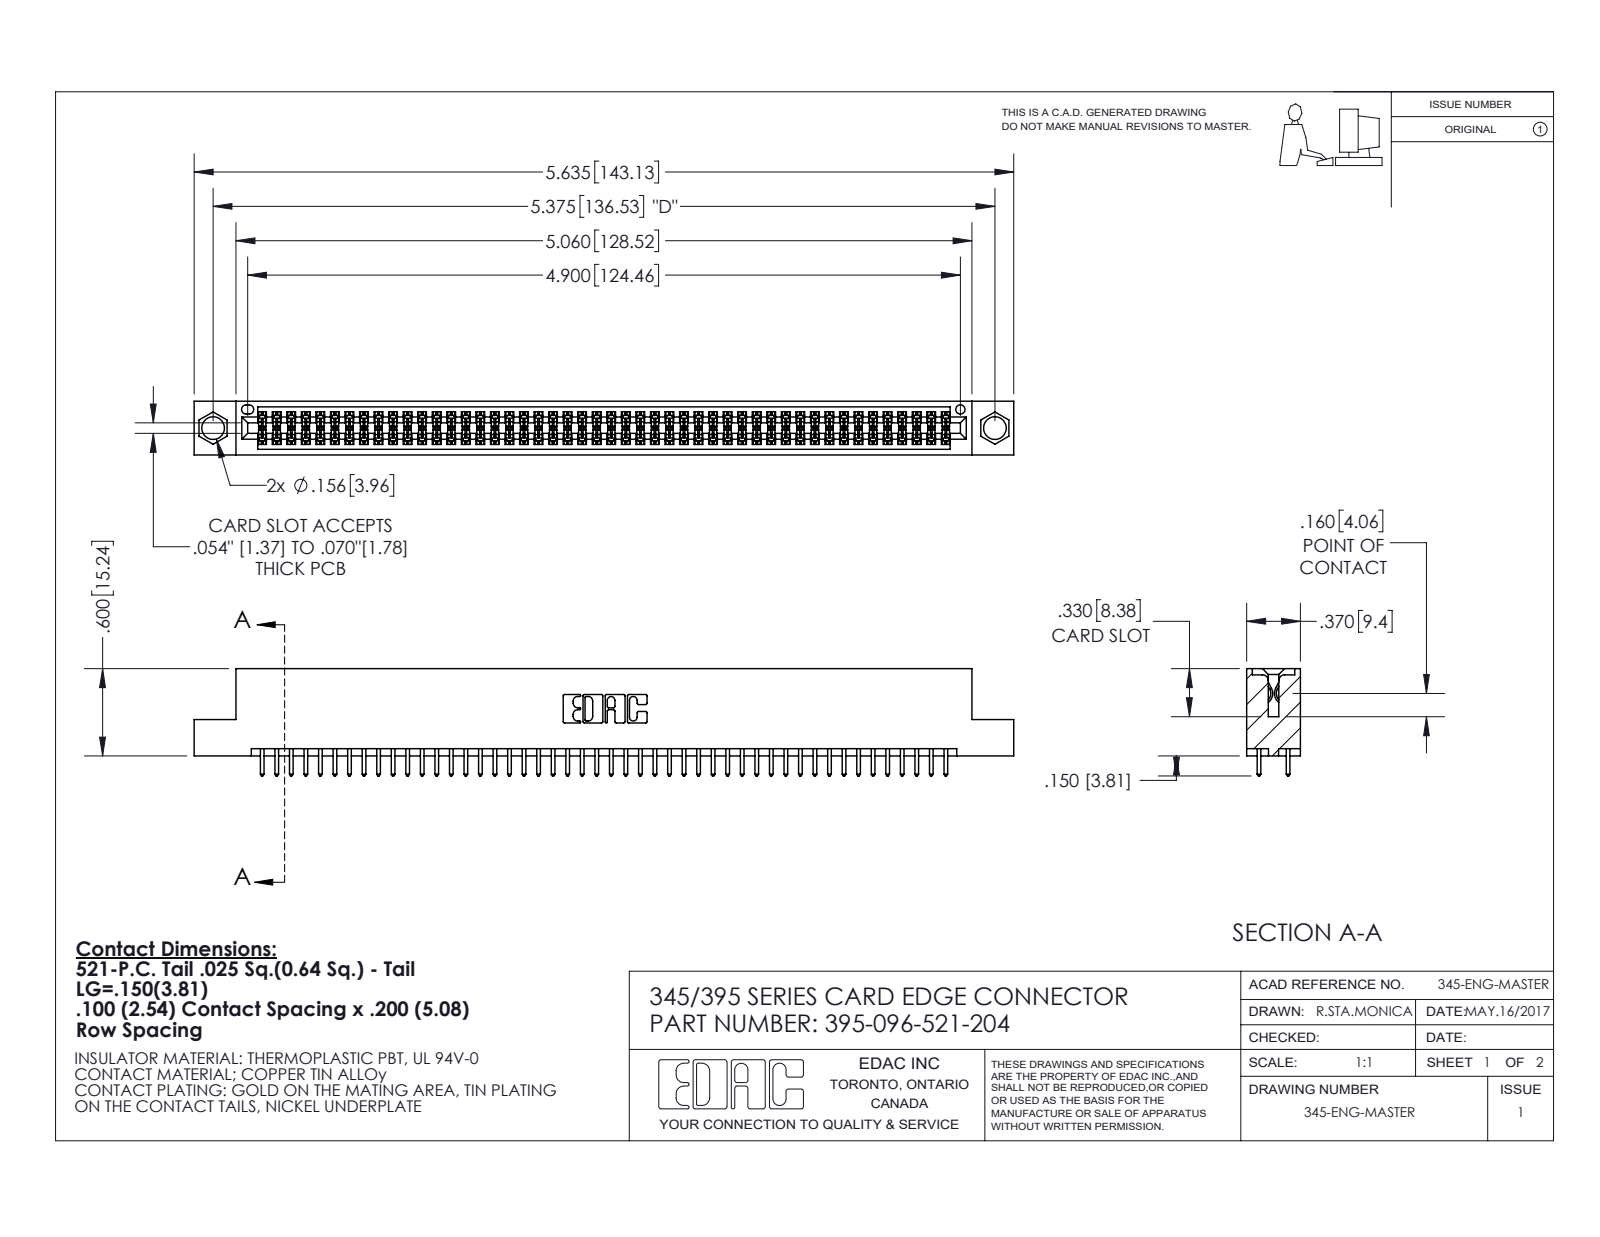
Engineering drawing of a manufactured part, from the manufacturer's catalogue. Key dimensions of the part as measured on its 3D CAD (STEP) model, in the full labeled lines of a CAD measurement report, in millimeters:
Part name (STEP PRODUCT): 345 Part_Flush Mounting Lugs - 0.156 Dia-TI; 395-096-521-204; 345-292-001_345-293-121
STEP written by: SolidWorks 2020 (CONFIG_CONTROL_DESIGN)
Units: millimetres
Bodies: 97 solids, 4940 faces (3262 planar, 1678 cylindrical, 0 other)
Overall size (bounding box): 143.1 × 18.7 × 9.4
Volume: 13 800 mm³ · Surface area: 20 140 mm²
Round holes (diameter × count): ⌀4 ×2, ⌀1.6 ×1
Partial cylindrical surfaces — rounded edges, fillets, slot ends (radius × count): R0.2 ×192, R0.3 ×96, R0.3 ×22, R0.2 ×6, R0.8 ×6, R0.7 ×3, R0.4 ×2, R0.5 ×2
Main face-to-face distances: 1.8, 7.6, 5.1, 9.4, 2.5, 6.9, 0.6, 5.7, 4.4, 3.8
Hole centre spacings: 6.9, 130.5, 136.5
